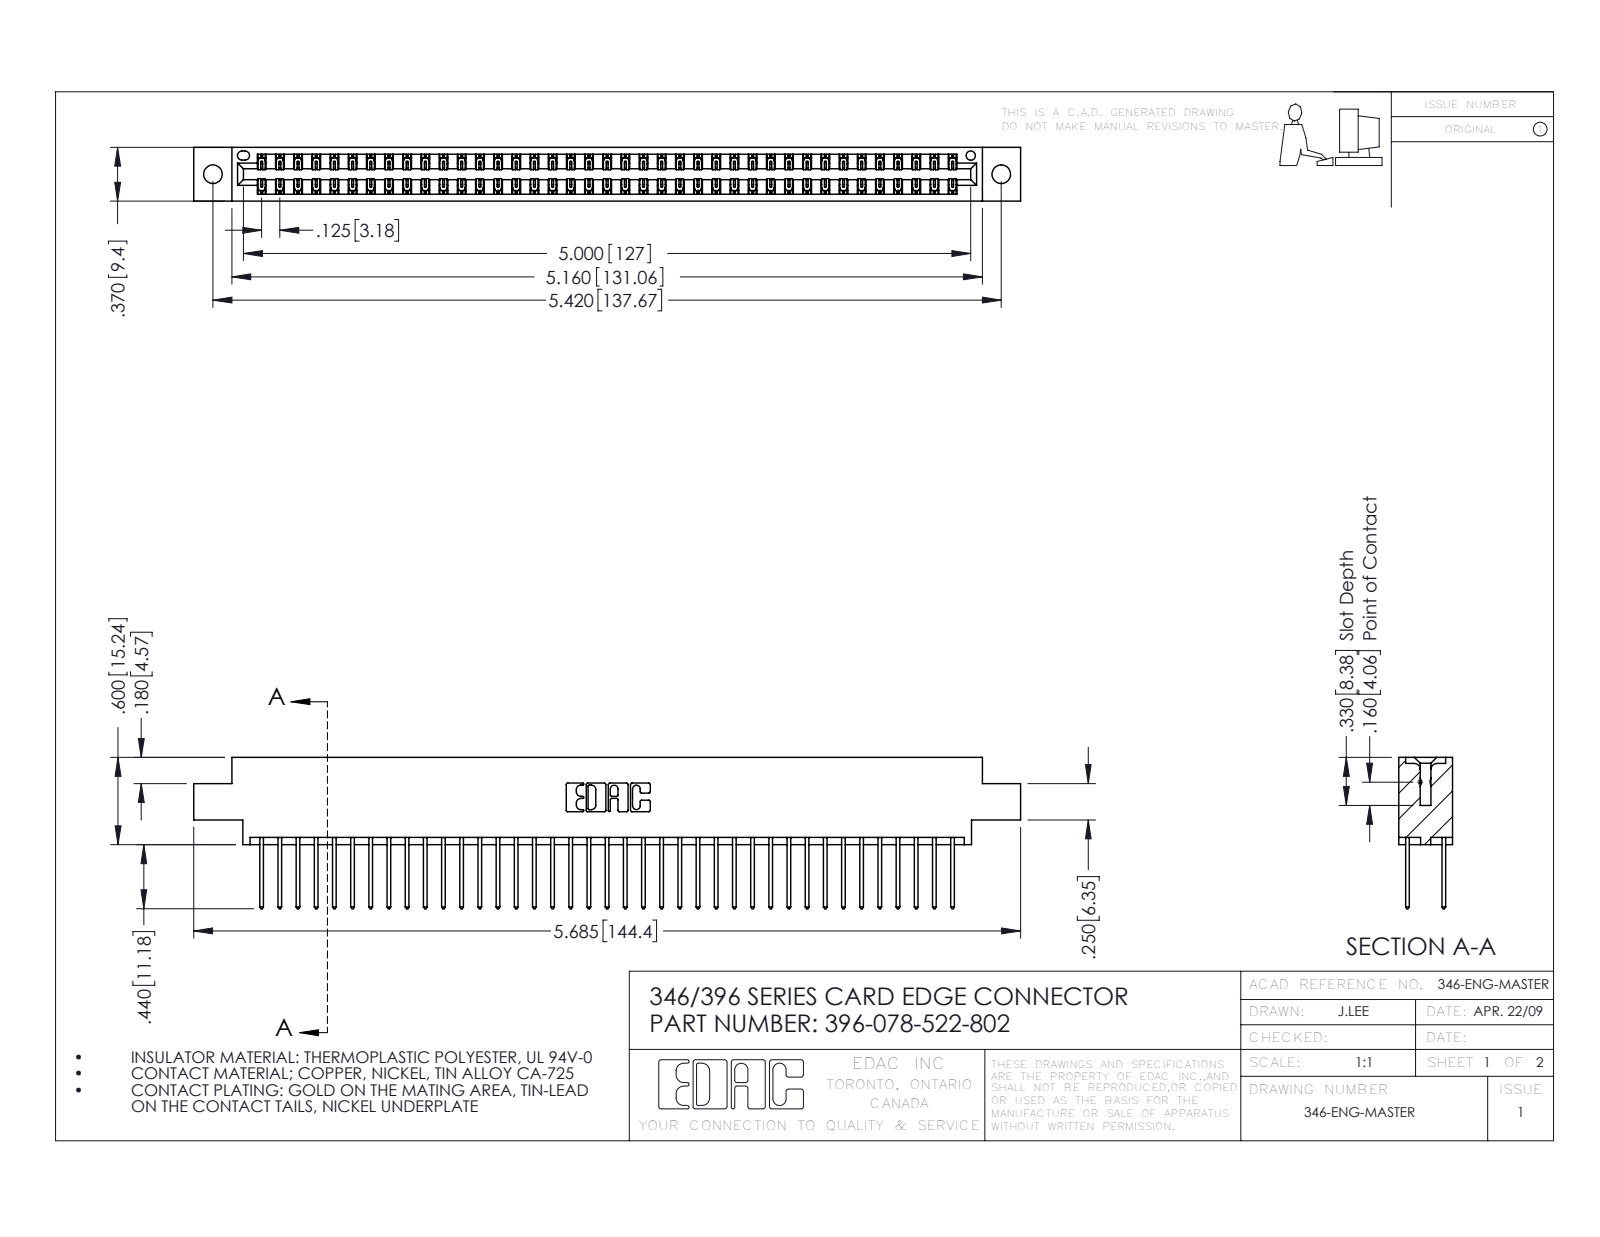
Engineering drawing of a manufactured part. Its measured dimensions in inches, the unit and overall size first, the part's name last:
Units: inches
Overall size (bounding box): 5.685 × 1.04 × 0.37
Round holes (diameter × count): ⌀0.128 ×2, ⌀0.064 ×1
Partial cylindrical surfaces — rounded edges, fillets, slot ends (radius × count): R0.006 ×117, R0.01 ×78, R0.01 ×22, R0.007 ×6, R0.031 ×6, R0.026 ×3, R0.014 ×2, R0.022 ×2
Main face-to-face distances: 0.048, 0.322, 0.25, 0.37, 0.072, 0.298, 0.025, 0.275, 0.148, 0.222
Hole centre spacings: 0.246, 5.211, 5.42
Volume: 0.858 in³ · Surface area: 31.19 in²
Bodies: 79 solids, 4182 faces (2810 planar, 1372 cylindrical, 0 other)
Part name (STEP PRODUCT): 346 Part_0.170 Offset - 0.128 Dia; 396-078-522-802; 345-292-001_345-293-122
STEP written by: SolidWorks 2016 (CONFIG_CONTROL_DESIGN)
